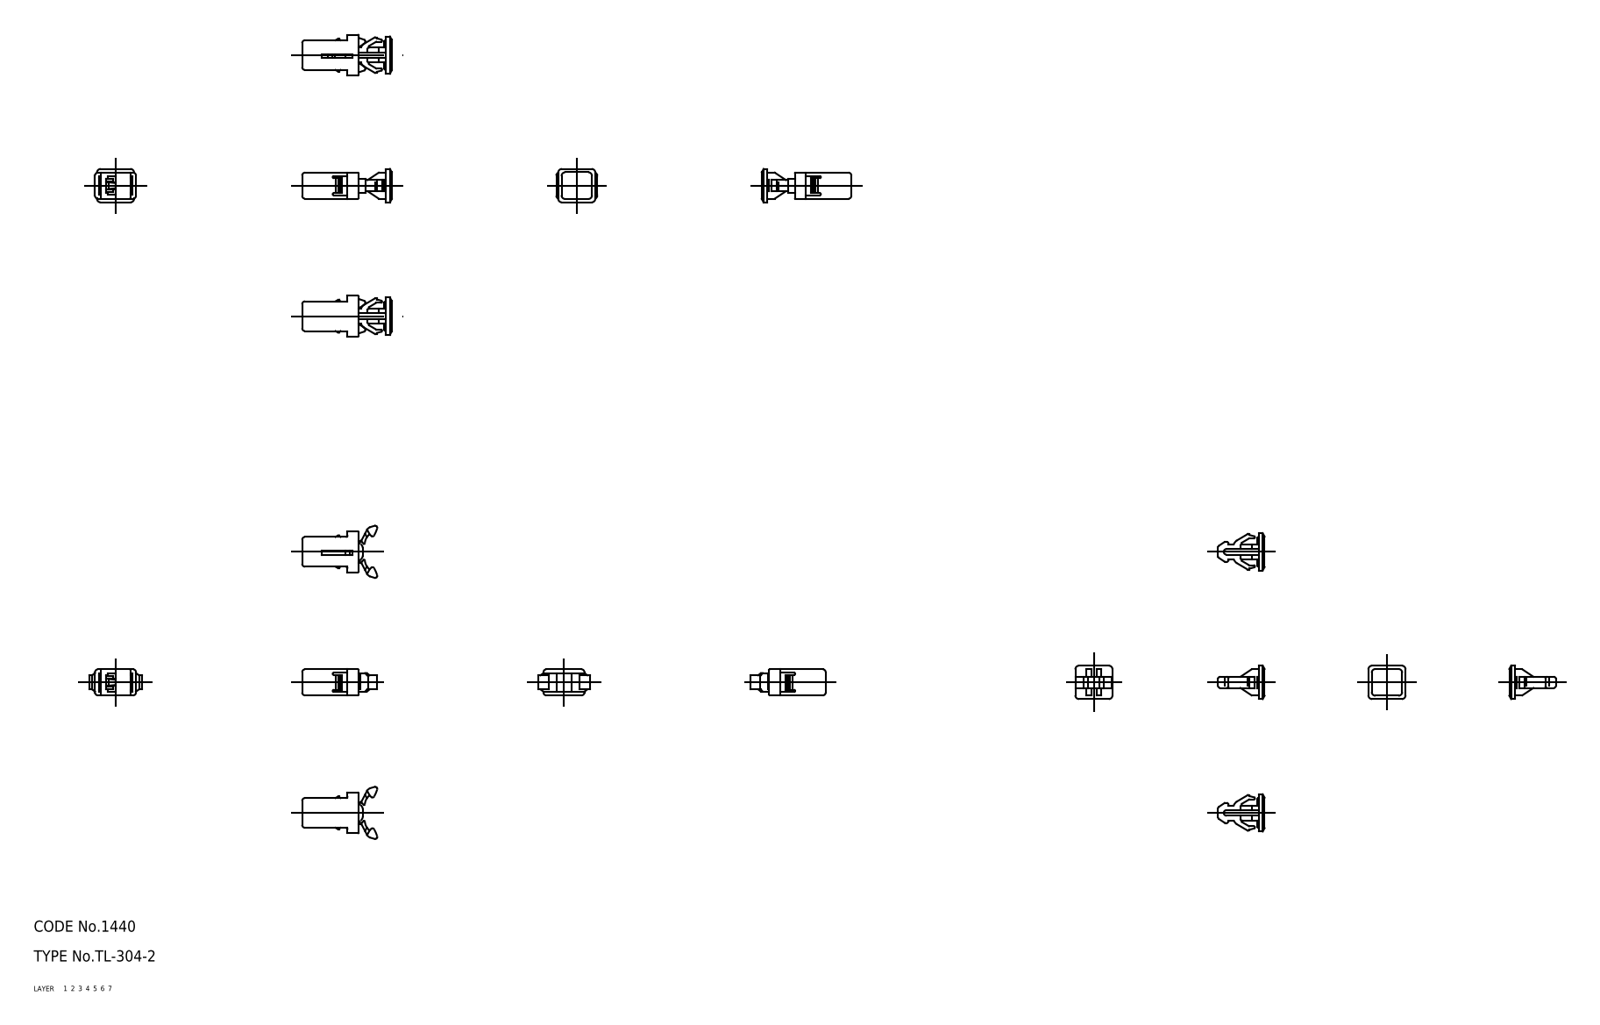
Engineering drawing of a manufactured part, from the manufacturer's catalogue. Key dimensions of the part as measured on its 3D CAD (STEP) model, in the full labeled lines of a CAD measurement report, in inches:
Part name (STEP PRODUCT): keeper; housing; arm; TL_304_2_8007_36
STEP written by: CADfix (AUTOMOTIVE_DESIGN)
Units: inches
Bodies: 3 solids, 236 faces (0 planar, 0 cylindrical, 236 other)
Overall size (bounding box): 1.69 × 0.553 × 0.354
Volume: 0.065 in³ · Surface area: 2.945 in²
